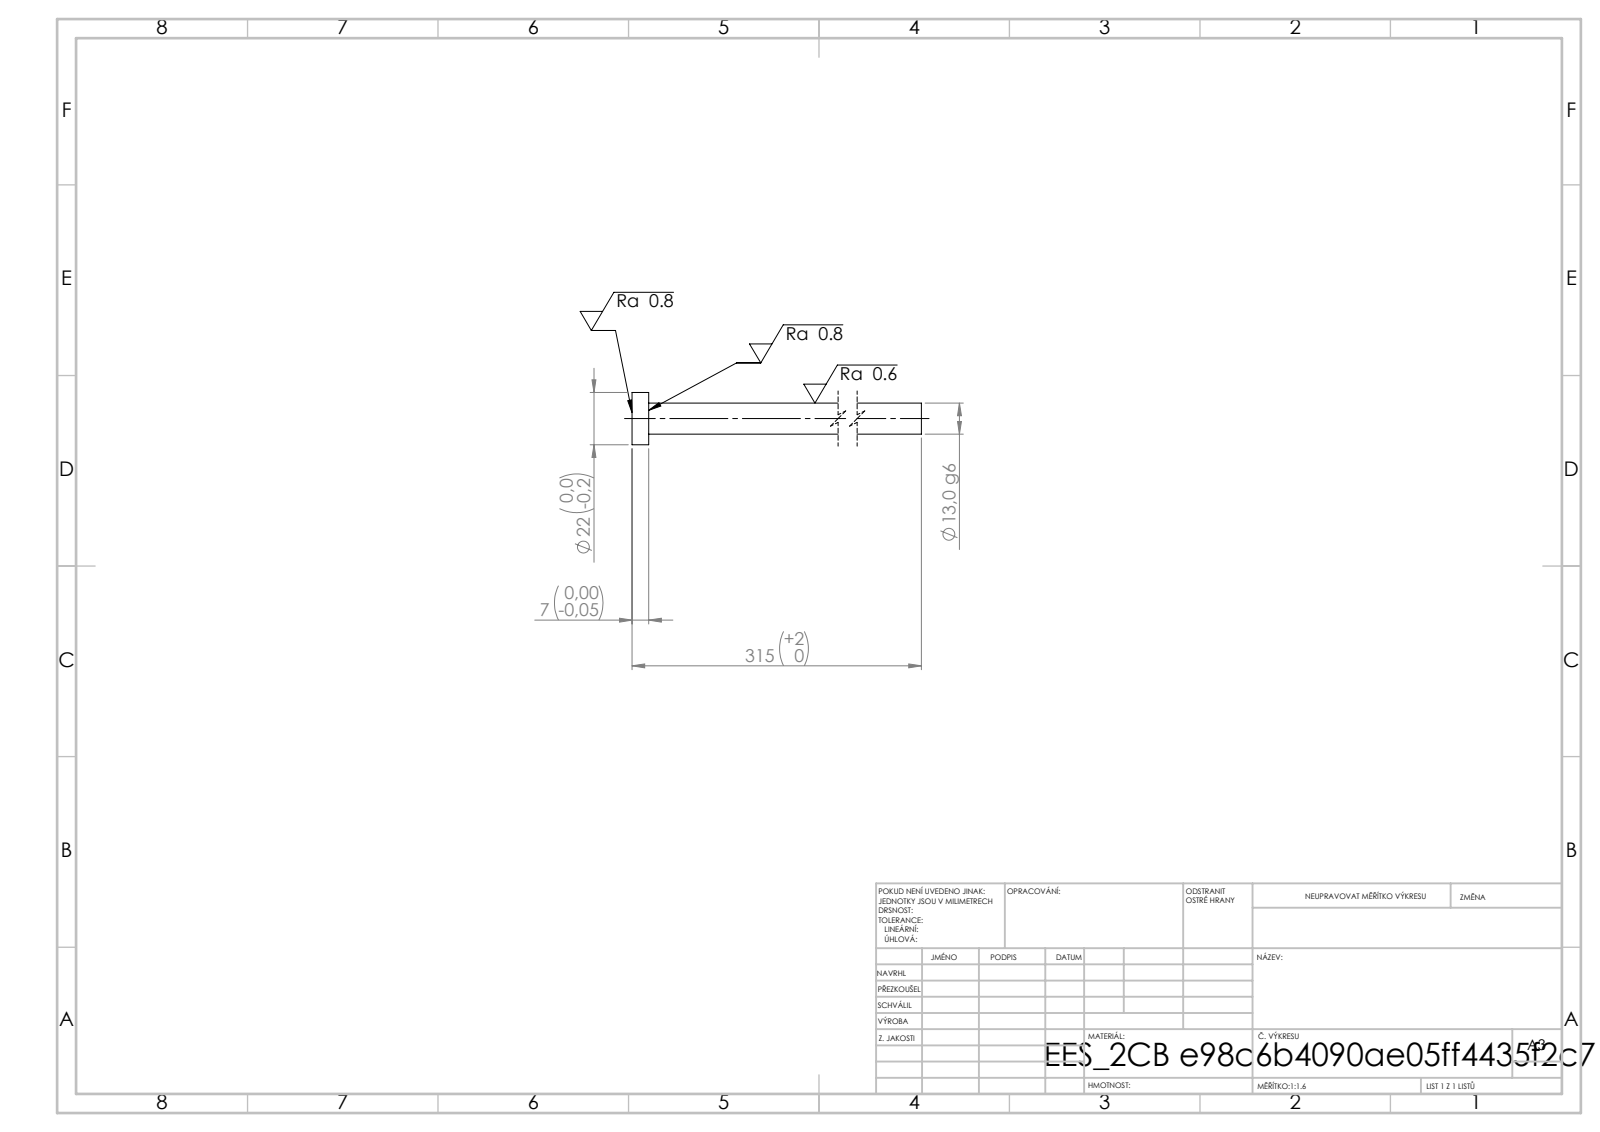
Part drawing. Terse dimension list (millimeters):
written by: SolidWorks 2019 (CONFIG_CONTROL_DESIGN)
unit: mm
bodies: 1 solid, 7 faces (3 planar, 4 cylindrical, 0 other)
size: 315 × 22 × 22
volume: 43 542 mm³; area: 13 823 mm²
bosses: 1× ⌀22, 1× ⌀13
face distances: 7, 315, 308
